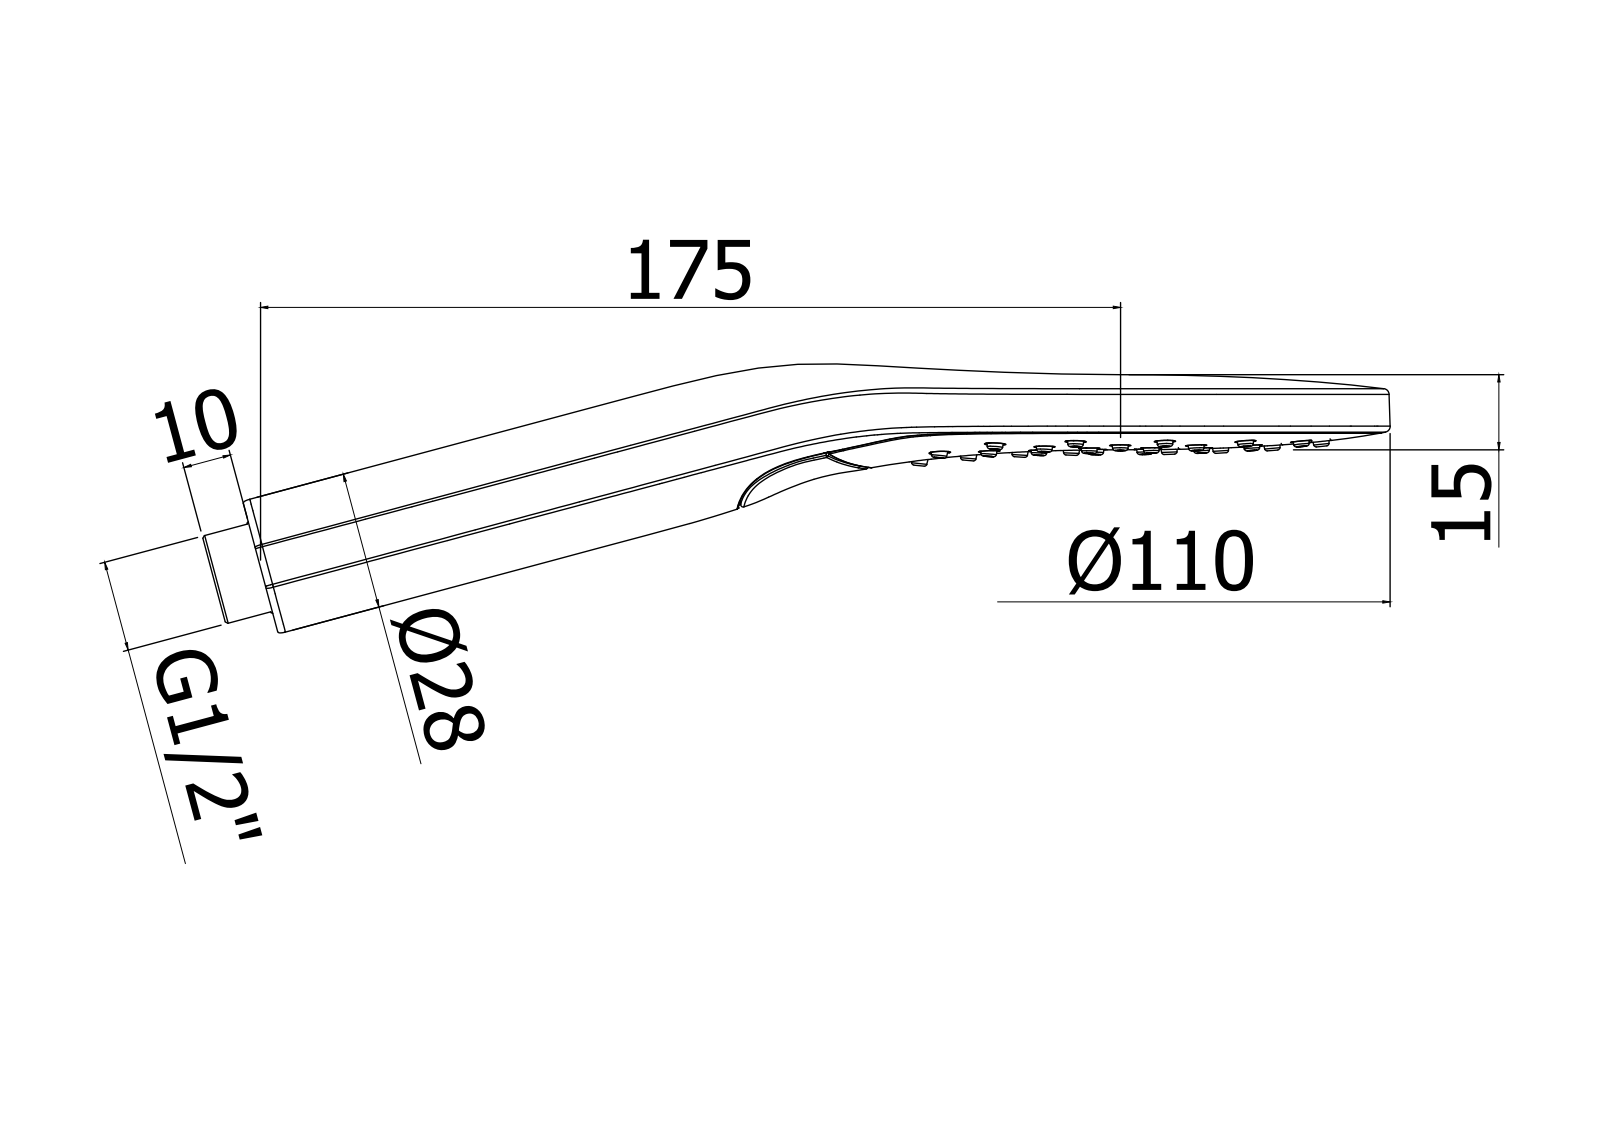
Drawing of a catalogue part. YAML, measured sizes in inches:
part_name: "4071084CR_E; 4071084CR_A; 4071084CR_B; 4071084CR_C (+8 more)"
step_written_by: "CREO PARAMETRIC BY PTC INC, 2020044 (CONFIG_CONTROL_DESIGN)"
units: inches
bodies: {solids: 9, faces: 2602, planar: 494, cylindrical: 391, other: 1717}
overall_size: [9.52, 4.328, 2.158]
volume: 2.086
surface_area: 140.4
round_holes:
  - {diameter: 0.236, count: 4}
  - {diameter: 0.157, count: 3}
  - {diameter: 0.028, count: 1}
  - {diameter: 0.106, count: 1}
  - {diameter: 0.118, count: 1}
  - {diameter: 0.26, count: 1}
  - {diameter: 0.37, count: 1}
  - {diameter: 0.394, count: 1}
  - {diameter: 0.408, count: 1}
  - {diameter: 0.433, count: 1}
  - {diameter: 0.449, count: 1}
  - {diameter: 0.472, count: 1}
round_bosses_or_shafts:
  - {diameter: 0.276, count: 4}
  - {diameter: 0.976, count: 1}
  - {diameter: 0.902, count: 1}
  - {diameter: 0.807, count: 1}
  - {diameter: 0.734, count: 1}
  - {diameter: 0.728, count: 1}
  - {diameter: 0.65, count: 1}
  - {diameter: 0.559, count: 1}
partial_cylinders:
  - {radius: 0.008, count: 44}
  - {radius: 0.02, count: 40}
  - {radius: 0.039, count: 24}
  - {radius: 0.012, count: 21}
  - {radius: 0.748, count: 12}
  - {radius: 0.728, count: 8}
  - {radius: 0.059, count: 5}
  - {radius: 0.016, count: 4}
face_to_face_distances: [0.059, 0.079, 0.394, 0.02, 0.327, 0.453, 0.13, 0.028, 0.217, 0.236]
hole_center_spacings: [1.417, 0.8, 0.627, 0.979, 1.473, 1.522, 1.769, 1.89]
